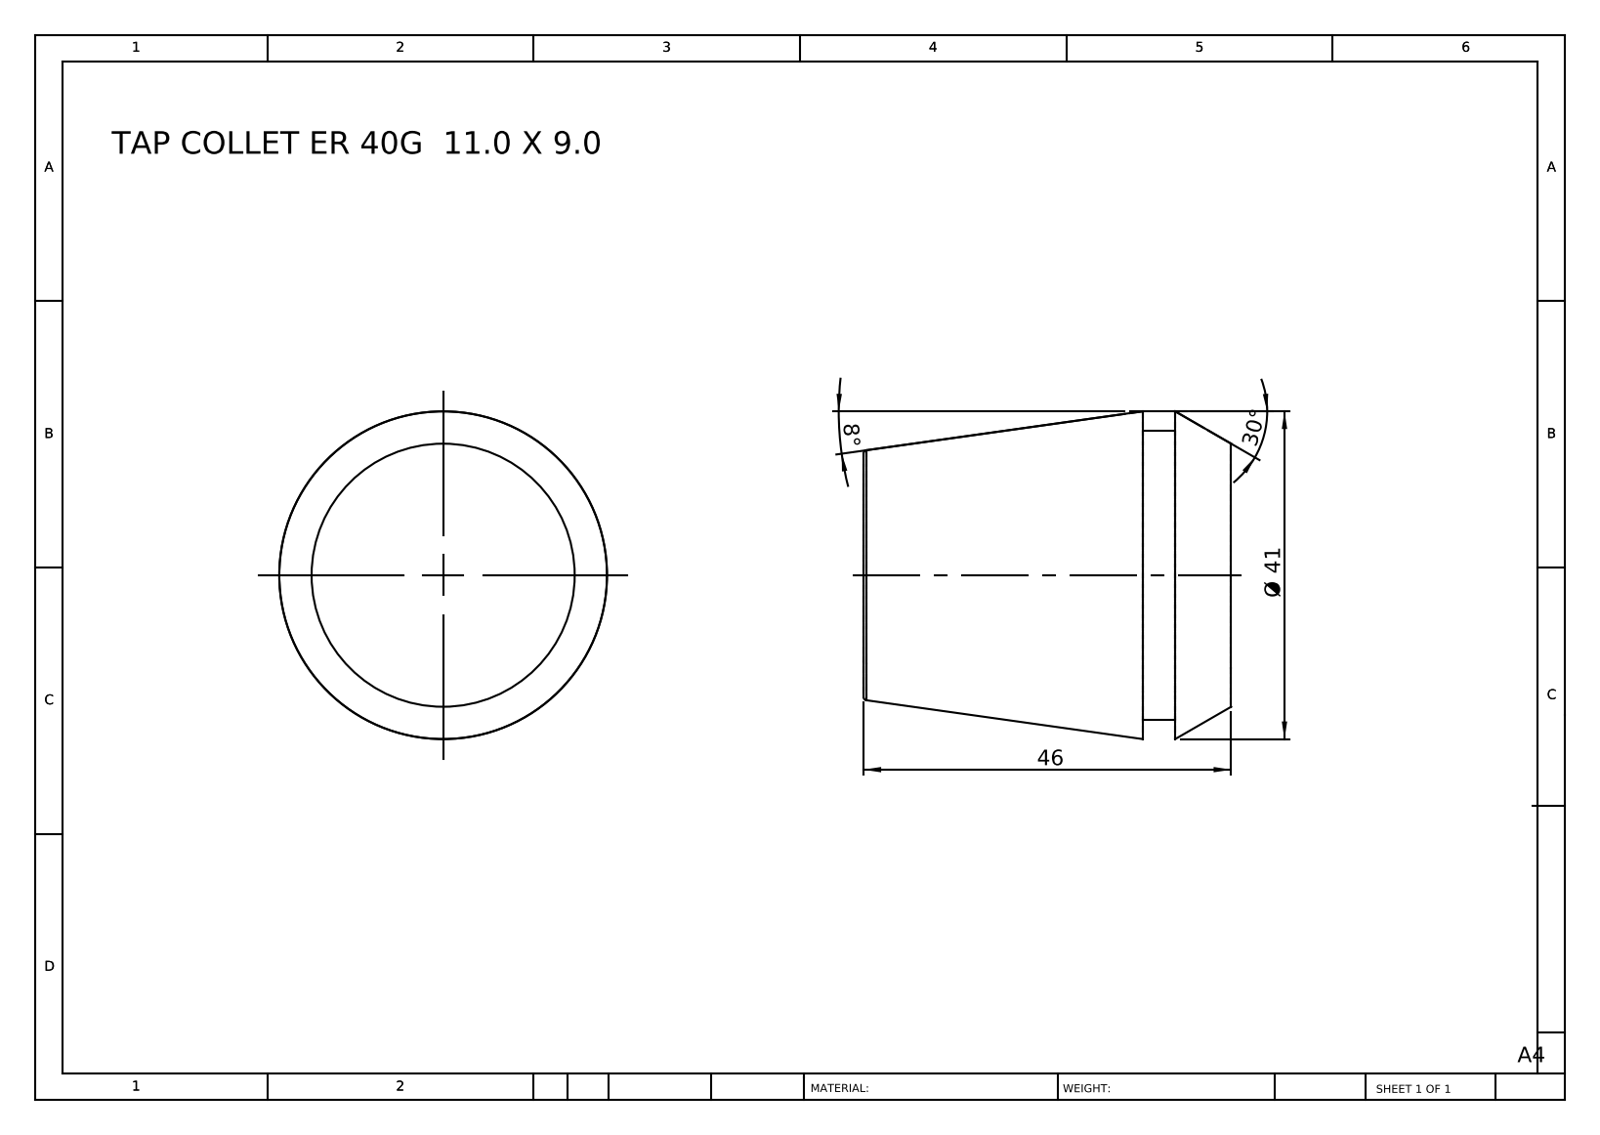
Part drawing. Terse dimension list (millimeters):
name: TAP COLLET ER 40G 11.0 X 9.0
written by: SolidWorks 2014 (CONFIG_CONTROL_DESIGN)
unit: mm
bodies: 1 solid, 12 faces (4 planar, 2 cylindrical, 6 other)
size: 46 × 41 × 41
volume: 47 690 mm³; area: 7 586 mm²
bosses: 1× ⌀36.2
face distances: 46, 11.1, 34.9, 7, 4.1, 39
